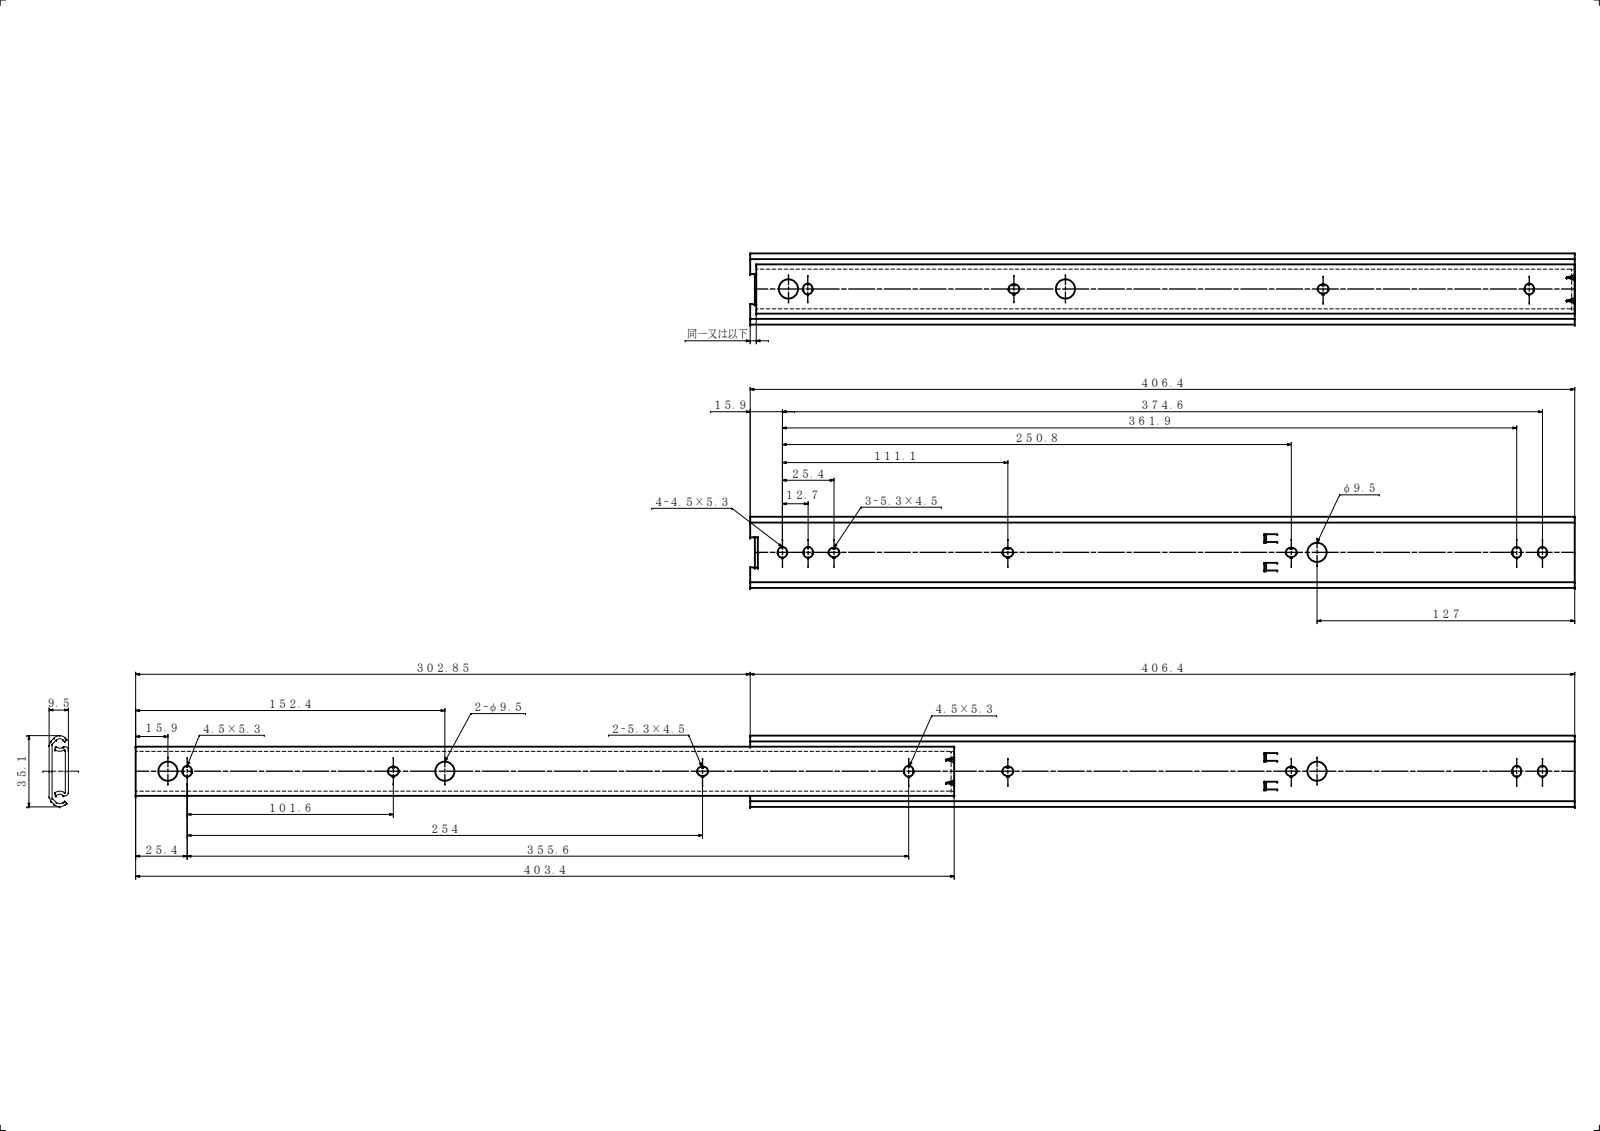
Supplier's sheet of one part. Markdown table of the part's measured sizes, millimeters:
| quantity | value |
| --- | --- |
| part name | U21-16; OM U21-16; IM U21-16 |
| STEP written by | SolidWorks 2019 (CONFIG_CONTROL_DESIGN) |
| units | millimeters |
| bodies | 2 solids, 135 faces (66 planar, 69 cylindrical, 0 other) |
| overall size | 709.25 × 35.1 × 9.5 |
| volume | 47 734 mm³ |
| surface area | 66 625 mm² |
| round holes (diameter × count) | 9.5 × 3 |
| partial cylindrical surfaces (radius × count) | 2.25 × 22, 0.4 × 6, 1 × 6, 3 × 6, 2 × 4, 0.3 × 2, 1.83 × 2, 2.38 × 2 |
| main face-to-face distances | 1.5, 8, 9.5, 6.5, 25.59, 4.88, 3.38, 24.09, 20.71, 27.09 |
| hole center spacings | 136.5, 429.85, 566.35 |
